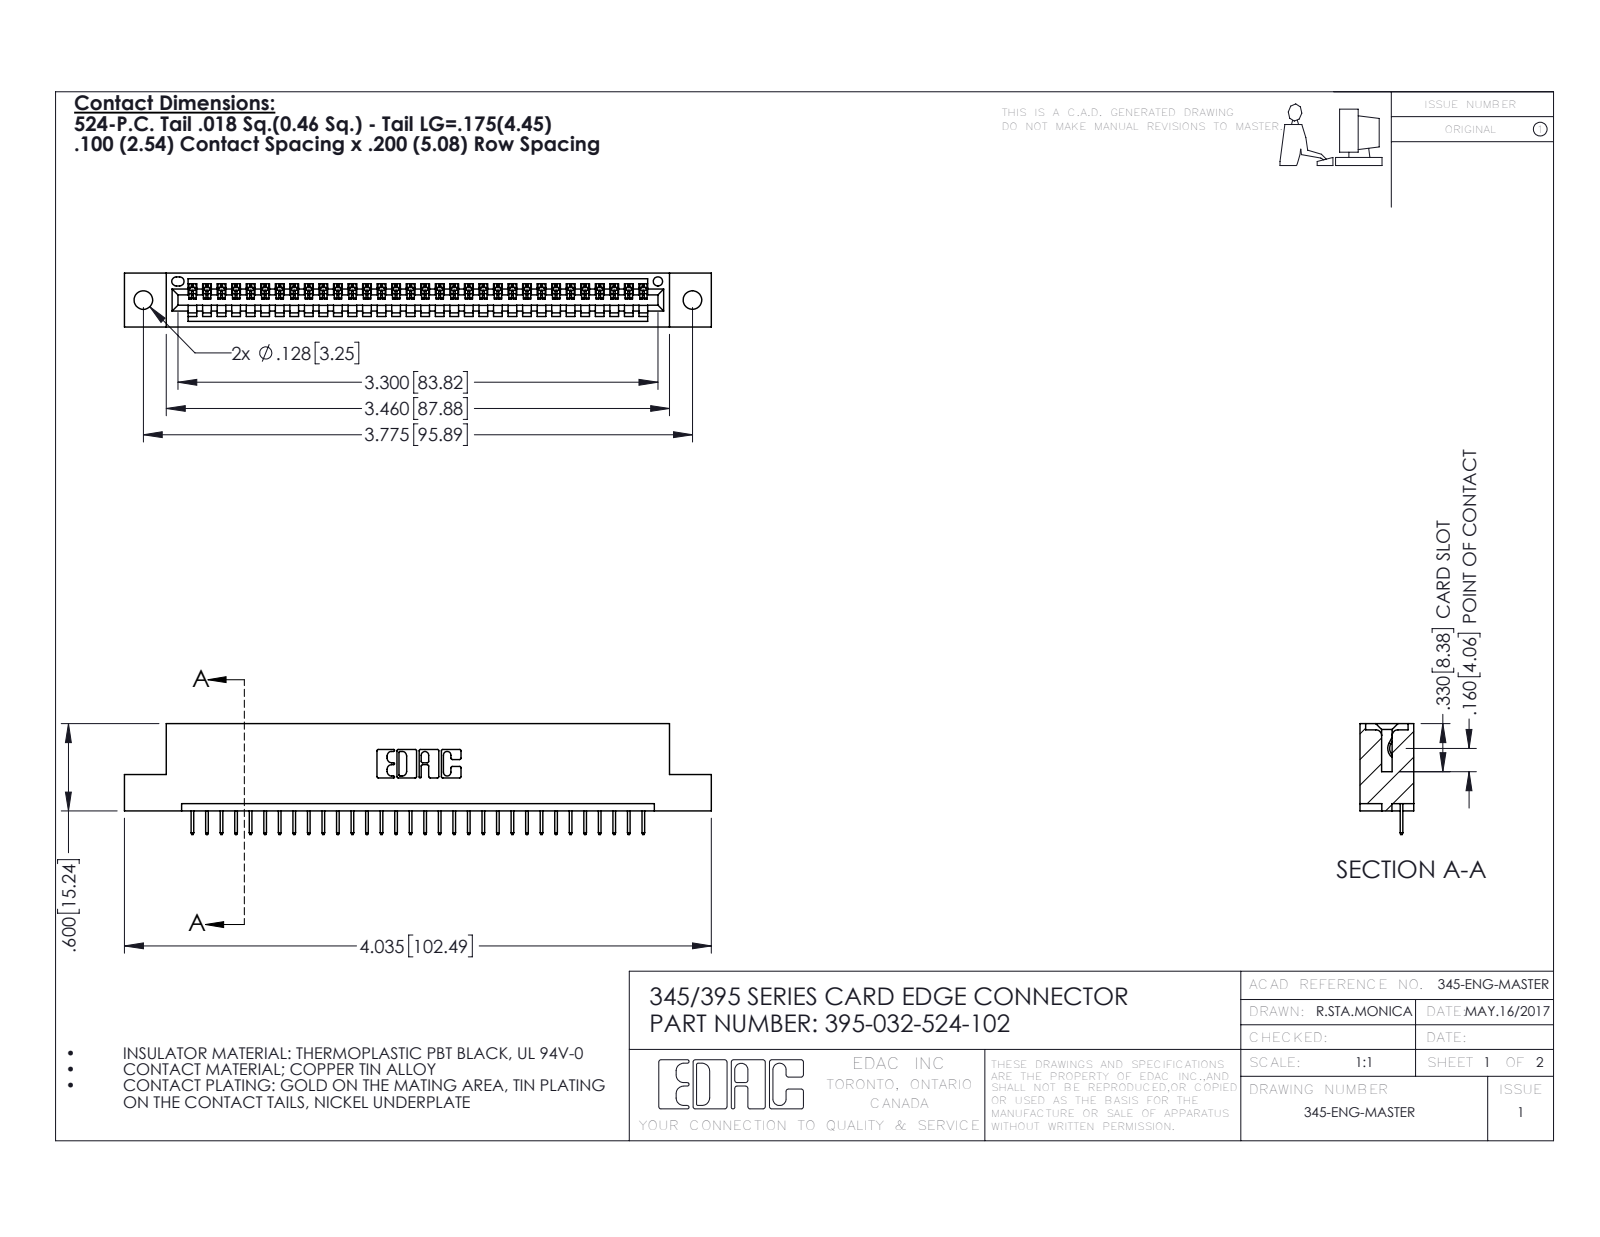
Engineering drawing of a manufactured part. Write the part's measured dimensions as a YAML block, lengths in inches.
part_name: "395-032-524-102; 345 Part_Flush Mounting Lugs - 0.128 Dia; 345-292-001_345-293-124"
step_written_by: "SolidWorks 2016 (CONFIG_CONTROL_DESIGN)"
units: inches
bodies: {solids: 33, faces: 2110, planar: 1552, cylindrical: 558, other: 0}
overall_size: [4.035, 0.762, 0.37]
volume: 0.579
surface_area: 18.29
round_holes:
  - {diameter: 0.128, count: 2}
  - {diameter: 0.064, count: 1}
partial_cylinders:
  - {radius: 0.006, count: 64}
  - {radius: 0.01, count: 22}
  - {radius: 0.007, count: 6}
  - {radius: 0.031, count: 6}
  - {radius: 0.026, count: 3}
  - {radius: 0.031, count: 2}
  - {radius: 0.04, count: 2}
  - {radius: 0.014, count: 1}
face_to_face_distances: [0.298, 0.072, 0.37, 0.2, 0.098, 0.272, 0.025, 0.225, 0.072, 0.149]
hole_center_spacings: [0.27, 3.54, 3.775]
